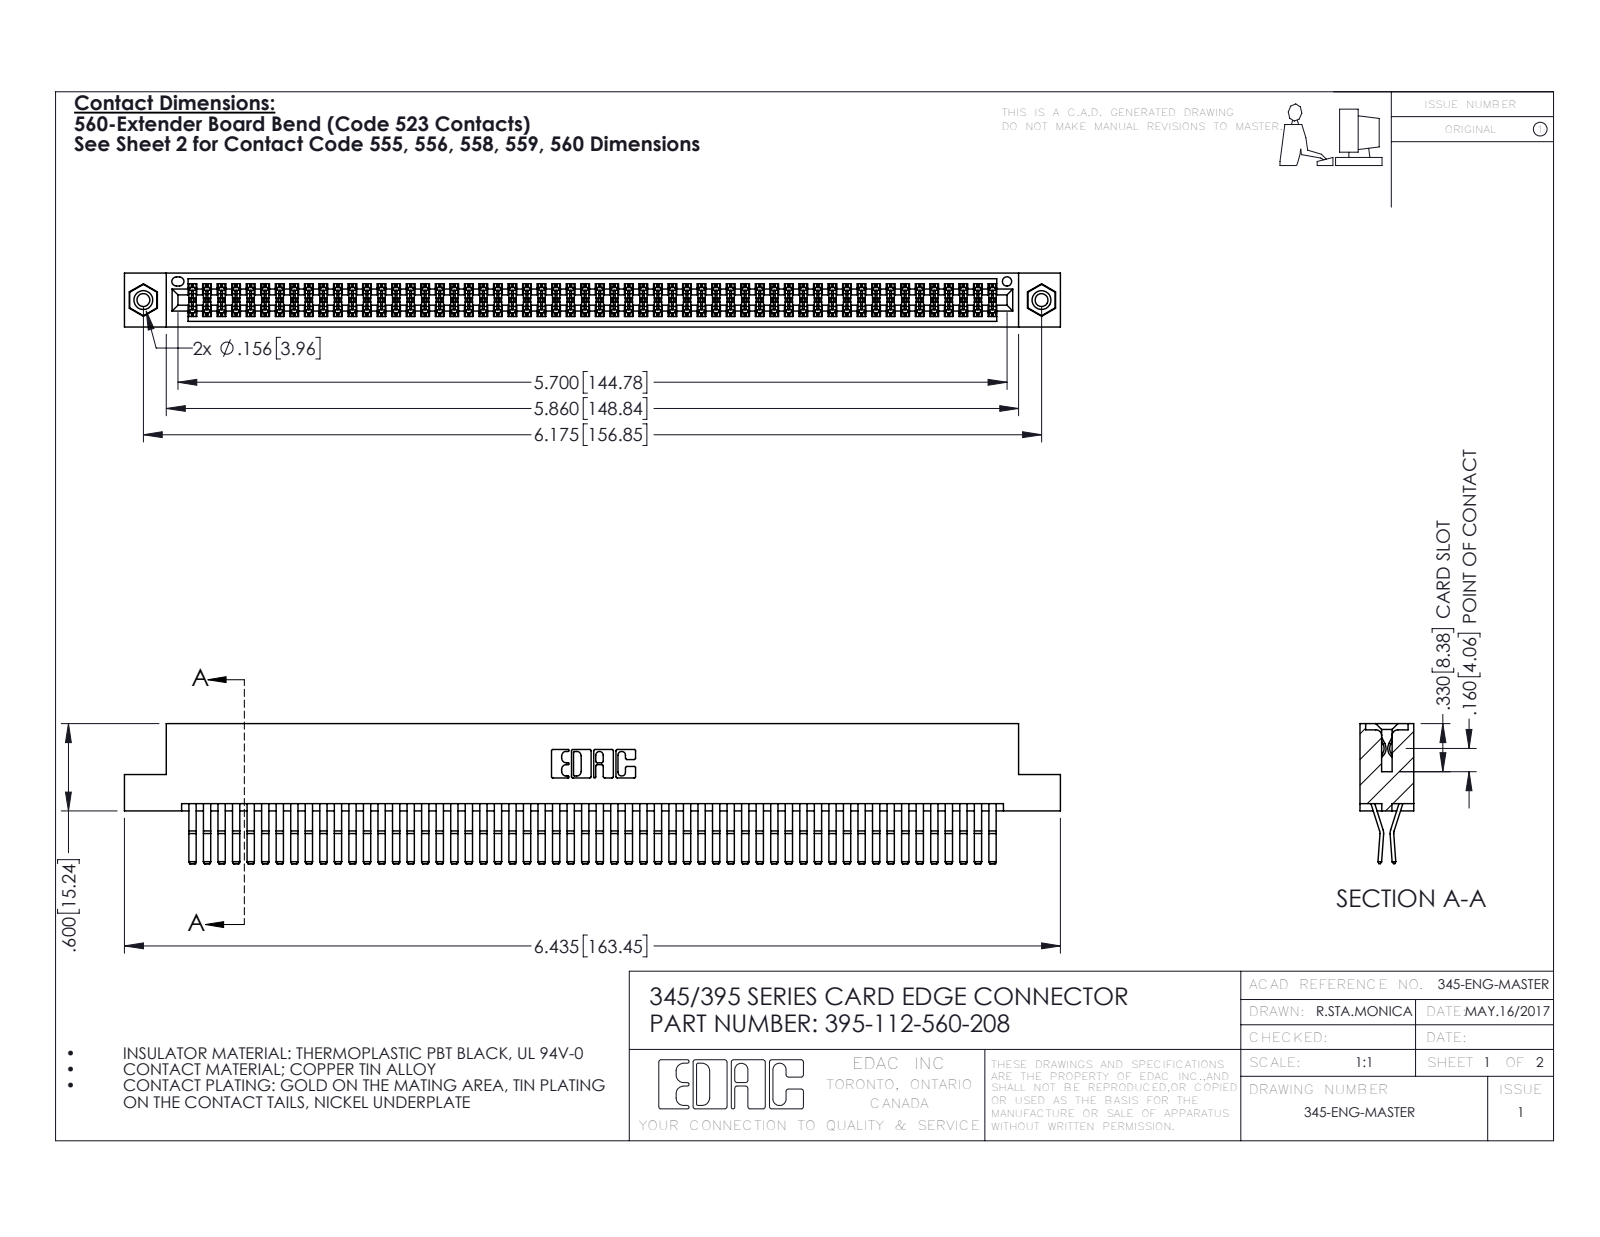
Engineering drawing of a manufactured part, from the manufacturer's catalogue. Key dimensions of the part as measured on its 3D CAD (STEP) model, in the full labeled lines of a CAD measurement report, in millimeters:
Part name (STEP PRODUCT): 395-112-560-208; 345-250-001_345-250-003-102; 345 Part_Flush Mounting Lugs - 0.156 Dia-TI; 345-292-001_560 Tail
STEP written by: SolidWorks 2016 (CONFIG_CONTROL_DESIGN)
Units: millimetres
Bodies: 115 solids, 6010 faces (3808 planar, 2186 cylindrical, 16 other)
Overall size (bounding box): 163.4 × 24.4 × 9.4
Volume: 16 730 mm³ · Surface area: 26 910 mm²
Round holes (diameter × count): ⌀2.3 ×2, ⌀3.2 ×2, ⌀4 ×2, ⌀1.6 ×1
Round bosses / shafts (diameter × count): ⌀3.9 ×2
Partial cylindrical surfaces — rounded edges, fillets, slot ends (radius × count): R0.2 ×168, R0.3 ×22, R0.2 ×6, R0.8 ×6, R0.7 ×3, R0.3 ×2, R0.4 ×2, R0.5 ×2
Main face-to-face distances: 0.6, 1.8, 7.6, 9.4, 5.1, 2.5, 6.9, 5.7, 4.4, 3.8
Hole centre spacings: 6.9, 150.9, 156.8
